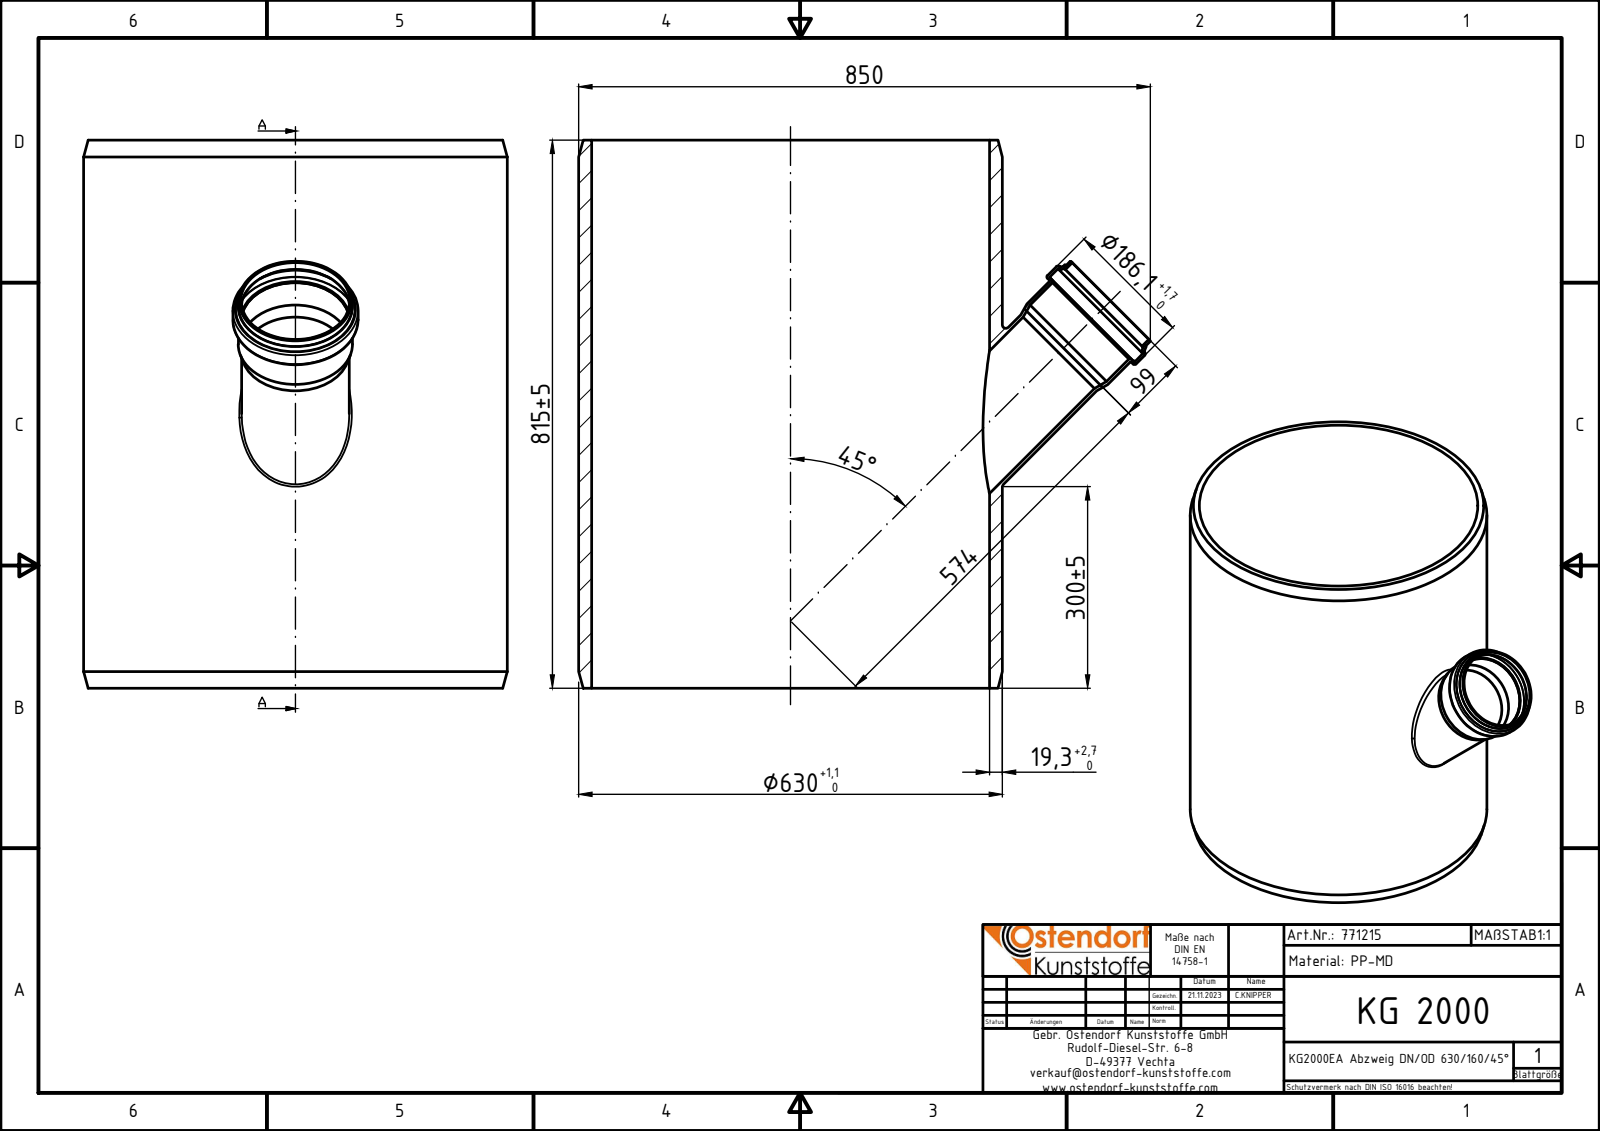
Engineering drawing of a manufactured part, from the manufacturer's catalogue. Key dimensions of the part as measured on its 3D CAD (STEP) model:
Part name (STEP PRODUCT): 771215z
STEP written by: Autodesk Inventor 2024 (AUTOMOTIVE_DESIGN)
Units: millimetres
Bodies: 1 solid, 42 faces (7 planar, 11 cylindrical, 24 other)
Overall size (bounding box): 850 × 815 × 630
Volume: 29 950 000 mm³ · Surface area: 3 388 000 mm²
Round holes (diameter × count): ⌀161 ×2, ⌀149.85 ×1, ⌀160.6 ×1, ⌀178.7 ×1, ⌀591.4 ×1
Round bosses / shafts (diameter × count): ⌀630 ×1, ⌀186.1 ×1, ⌀169.6 ×1, ⌀168.4 ×1, ⌀160 ×1
Main face-to-face distances: 815, 42.7, 24.7, 18, 31.61, 6.91, 11.09, 0.81, 23.89, 30.8
